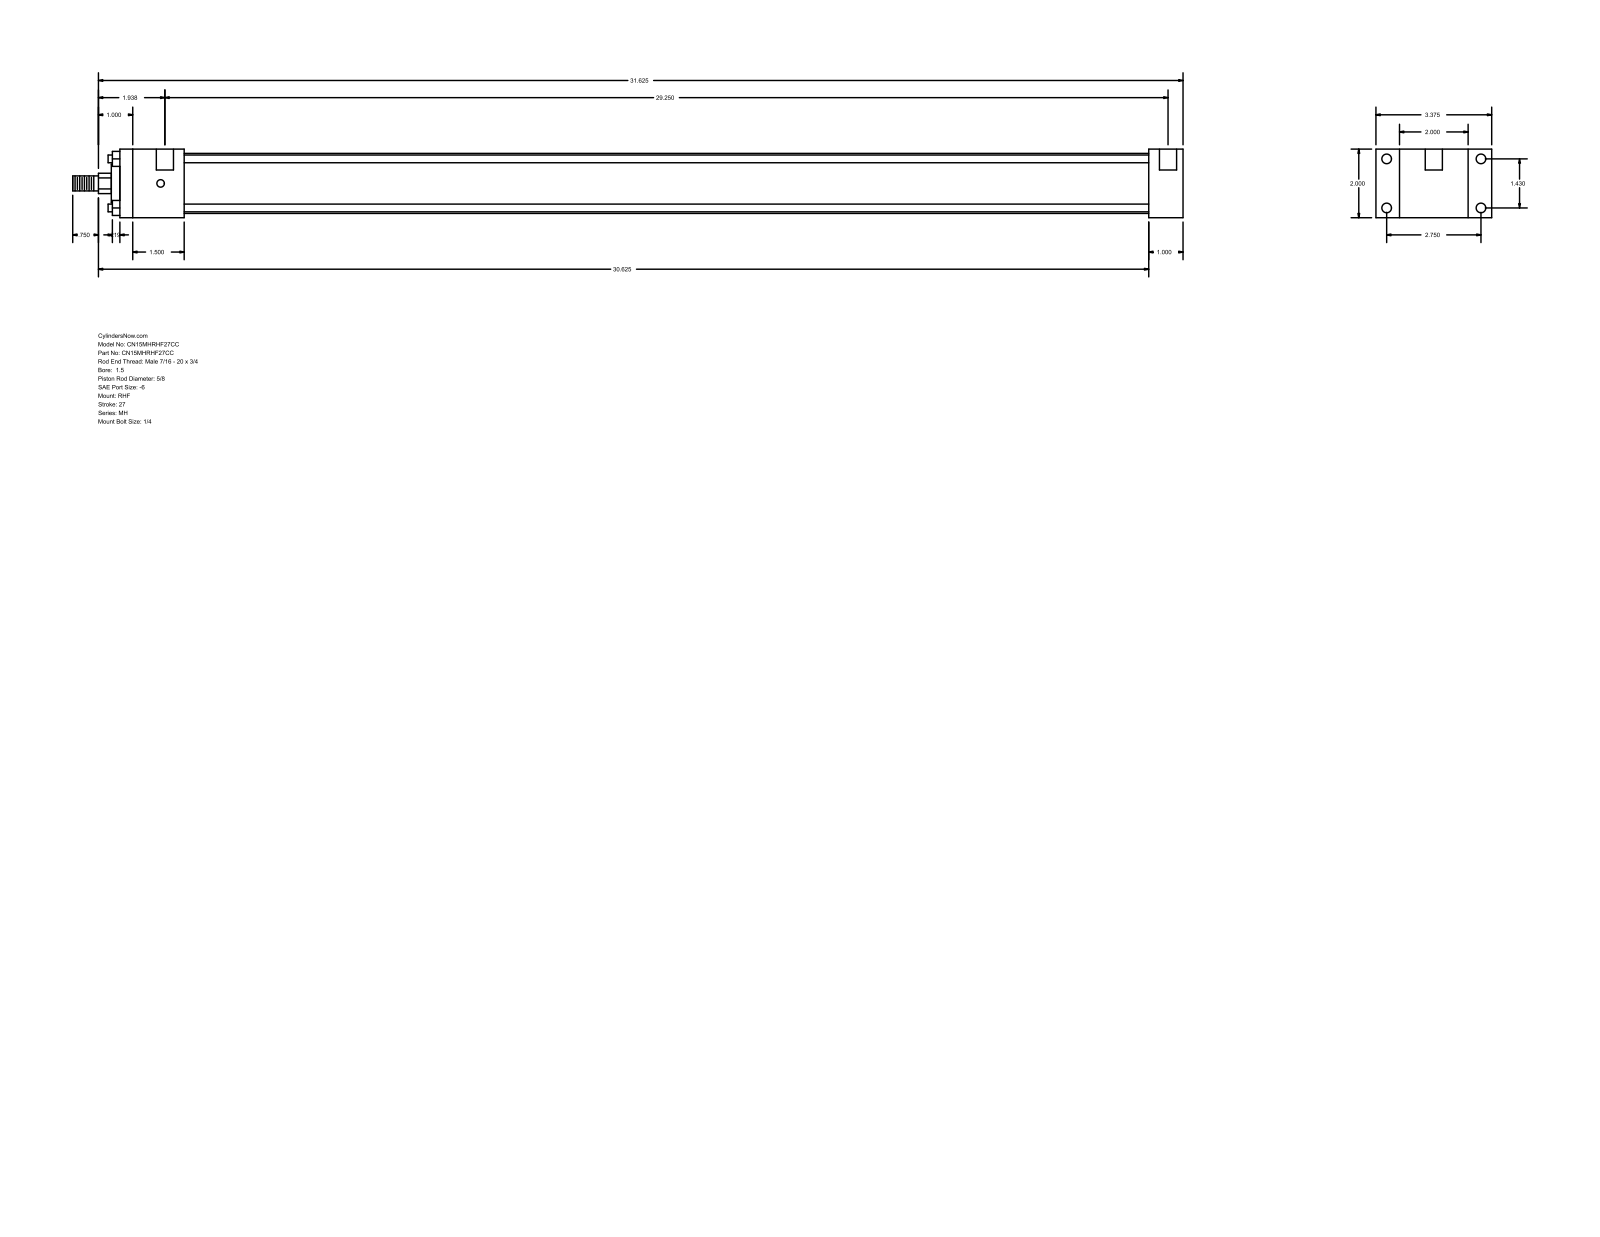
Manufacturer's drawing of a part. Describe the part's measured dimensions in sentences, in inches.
The part is named "MH_RHF__0150_0.625". Its 3-D file was written by "GSSL Pune (CONFIG_CONTROL_DESIGN)". It is 0 solids with 88 faces: 60 planar, 28 cylindrical and 0 other. Overall it measures 32.375 by 3.375 by 2 inches. Round holes: 4 of diameter 0.219, 4 of diameter 0.281, 2 of diameter 0.5. Round bosses or shafts: 4 of diameter 0.225, 1 of diameter 1.75, 1 of diameter 1.125, 1 of diameter 0.625, 1 of diameter 0.437. Partial cylindrical surfaces (rounded edges, fillets, slot ends): 1 of radius 0.297. The main face-to-face distances are 2, 0.687, 2.687, 1, 30, 31, 3.375, 1.875, 28.125, 29.125. The hole center spacings are 1.43, 2.75, 3.099, 29.375, 0.125, 29.25.
